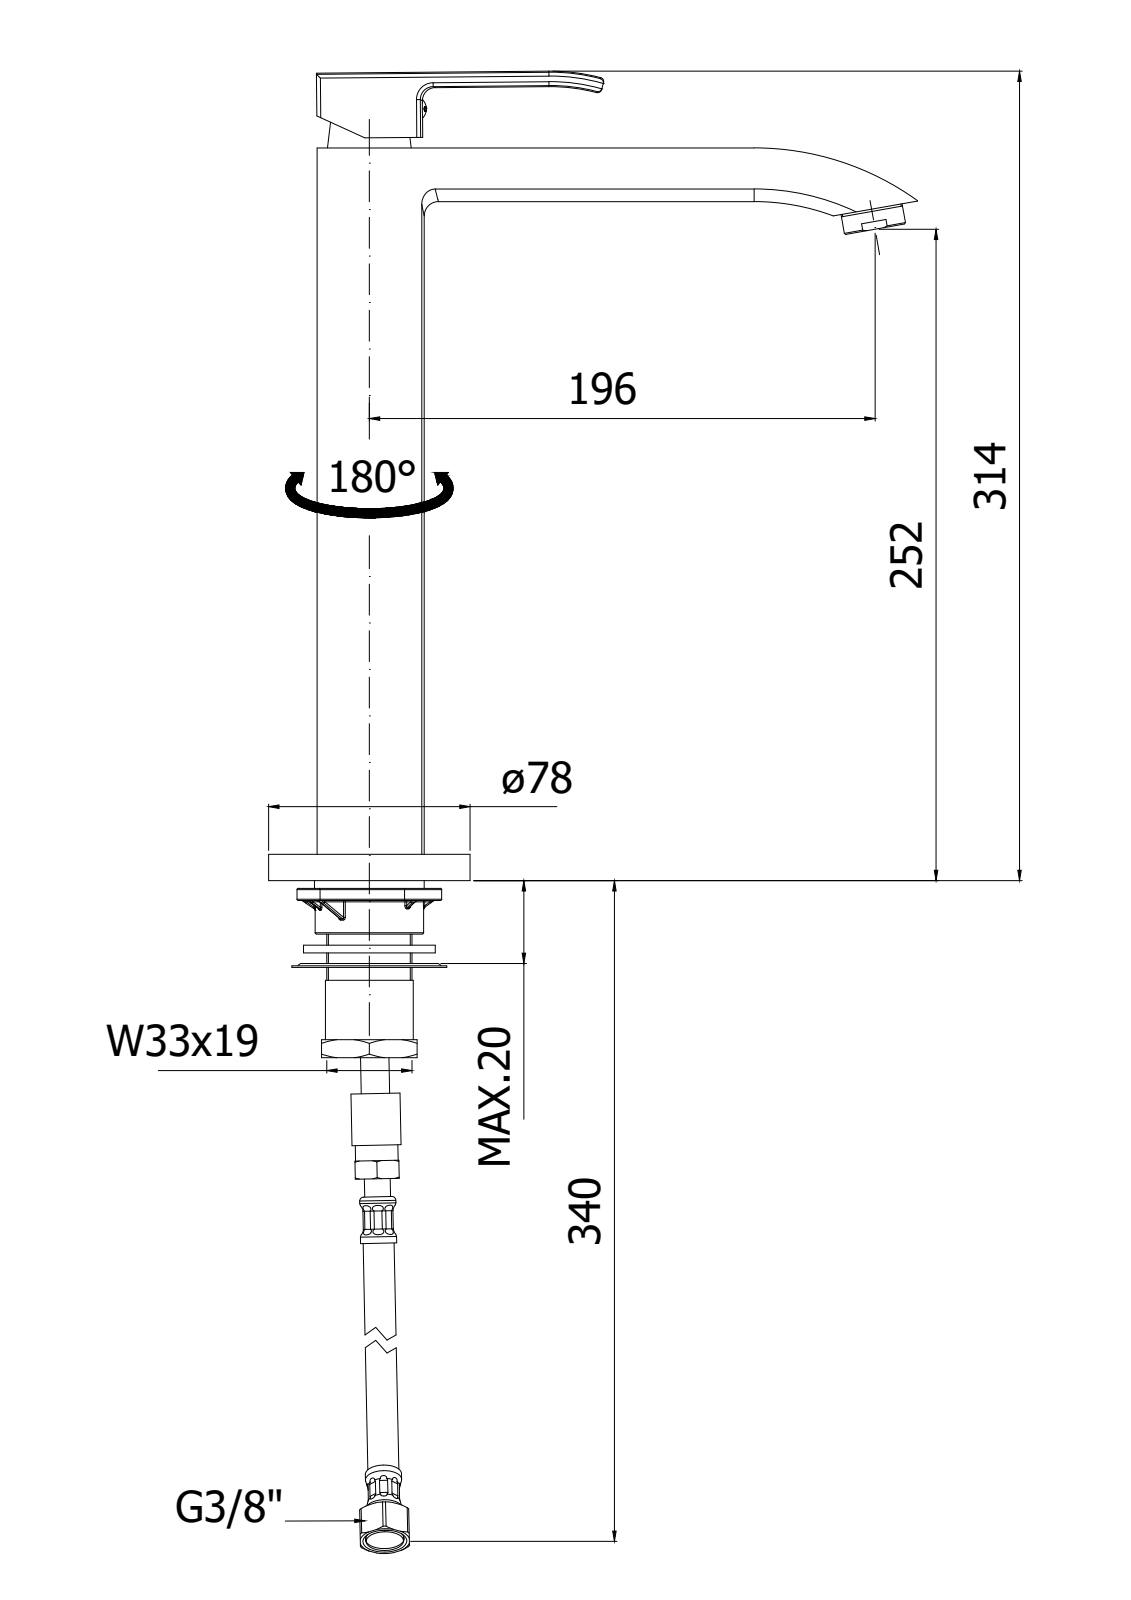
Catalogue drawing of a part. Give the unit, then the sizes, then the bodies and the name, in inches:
Units: inches
Overall size (bounding box): 12.344 × 9.893 × 3.071
Round holes (diameter × count): ⌀0.138 ×2, ⌀0.236 ×2, ⌀0.413 ×2, ⌀0.63 ×2, ⌀0.118 ×1, ⌀0.165 ×1, ⌀0.217 ×1, ⌀0.307 ×1, ⌀0.657 ×1, ⌀0.669 ×1, ⌀0.756 ×1, ⌀0.787 ×1
Round bosses / shafts (diameter × count): ⌀0.197 ×4, ⌀0.118 ×4, ⌀0.394 ×2, ⌀3.071 ×1, ⌀2.941 ×1, ⌀2.382 ×1, ⌀2.362 ×1, ⌀2.165 ×1
Partial cylindrical surfaces — rounded edges, fillets, slot ends (radius × count): R0.02 ×66, R0.012 ×34, R0.079 ×17, R0.039 ×16, R0.118 ×12, R0.028 ×10, R0.01 ×8, R0.059 ×8
Main face-to-face distances: 0.118, 1.28, 1.398, 1.161, 11.173, 0.236, 0.157, 0.079, 10.772, 0.126
Hole centre spacings: 1.299, 0.696, 0.972, 1.844, 0.02, 0.682, 0.711, 1.393
Volume: 15.56 in³ · Surface area: 258.6 in²
Bodies: 3 solids, 2644 faces (1755 planar, 477 cylindrical, 412 other)
Part name (STEP PRODUCT): LES188CR
STEP written by: CREO PARAMETRIC BY PTC INC, 2020044 (CONFIG_CONTROL_DESIGN)
